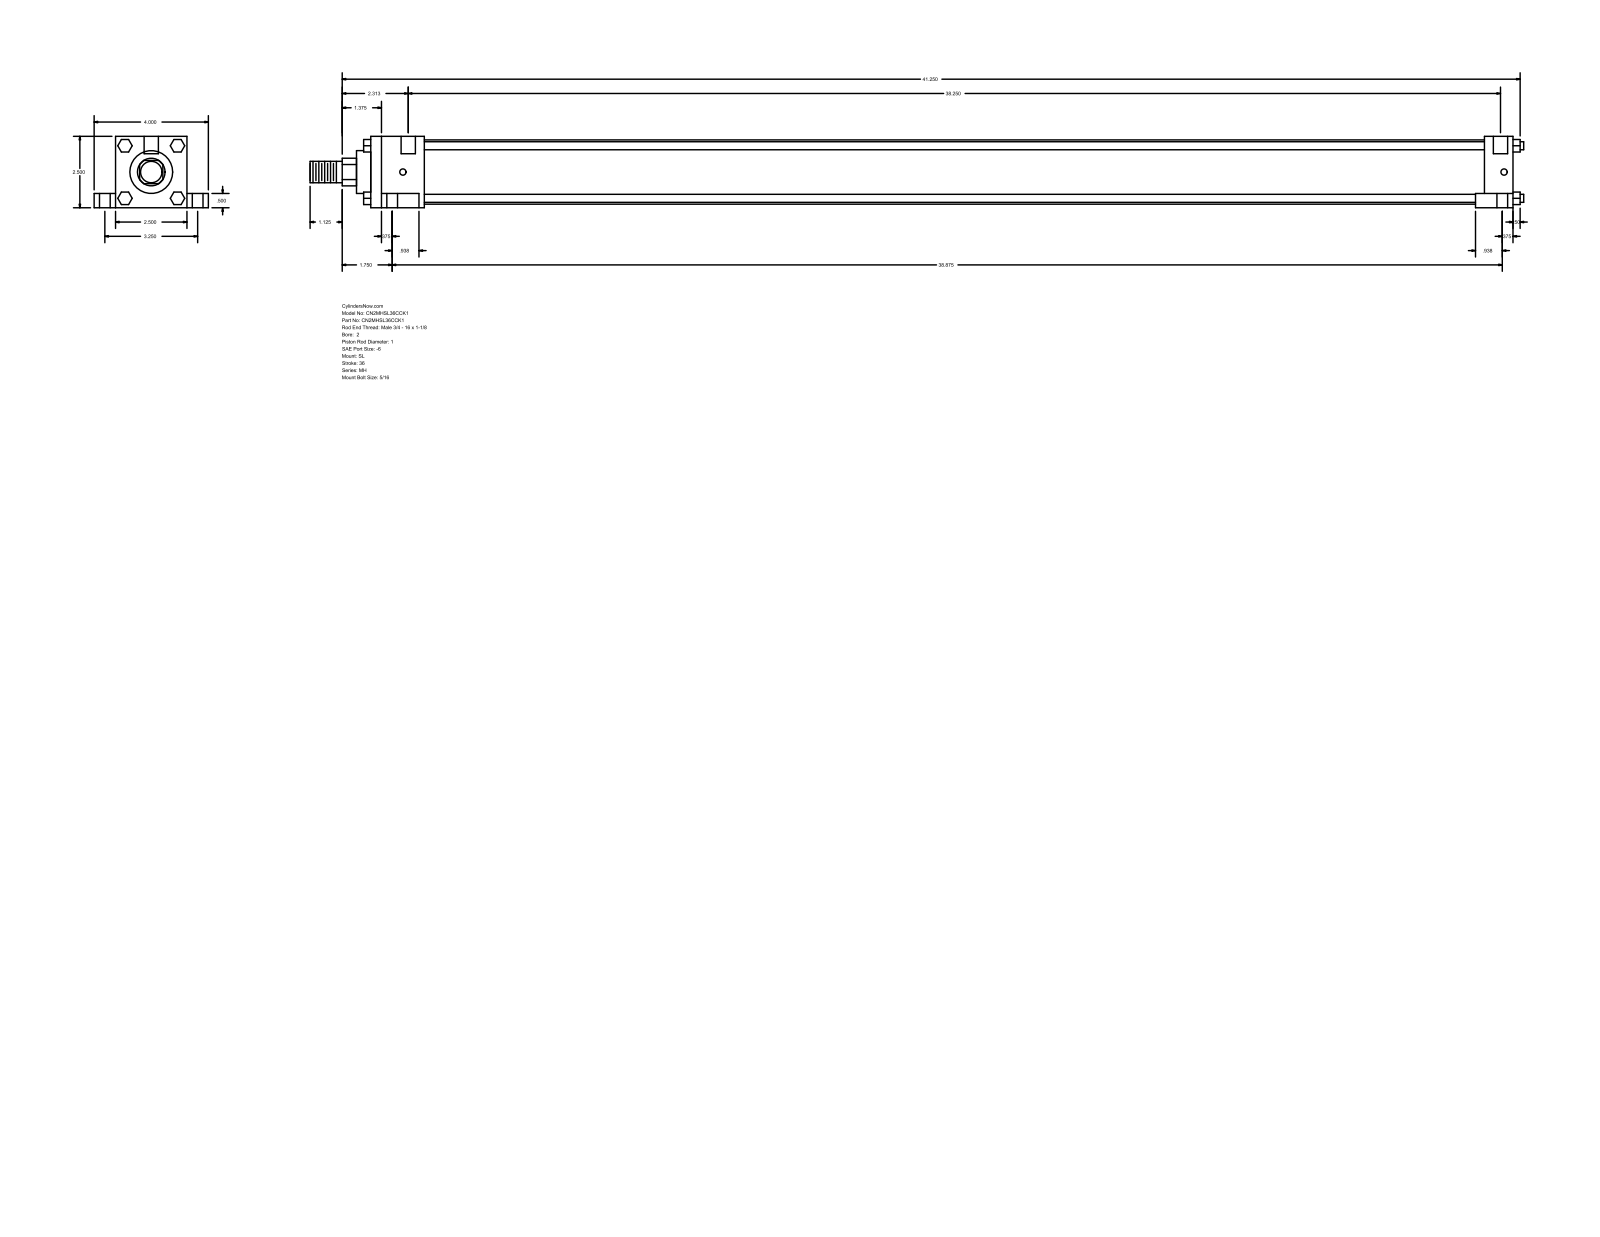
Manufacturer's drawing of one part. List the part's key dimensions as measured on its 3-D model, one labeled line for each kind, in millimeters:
Part name (STEP PRODUCT): MH_SL__0200_1
STEP written by: GSSL Pune (CONFIG_CONTROL_DESIGN)
Units: millimetres
Bodies: 0 solids, 148 faces (112 planar, 36 cylindrical, 0 other)
Overall size (bounding box): 1079.5 × 101.6 × 63.5
Round holes (diameter × count): ⌀5.56 ×4, ⌀9.53 ×4, ⌀15.88 ×4, ⌀12.7 ×2
Round bosses / shafts (diameter × count): ⌀7.14 ×4, ⌀57.15 ×1, ⌀38.1 ×1, ⌀25.4 ×1, ⌀19.05 ×1
Partial cylindrical surfaces — rounded edges, fillets, slot ends (radius × count): R12.29 ×1
Main face-to-face distances: 63.5, 1016, 12.7, 19.05, 50.8, 82.55, 25.4, 990.6, 47.63, 942.97
Hole centre spacings: 41.3, 42.36, 43.67, 82.54, 974.01, 978.77, 979.48, 986.7
